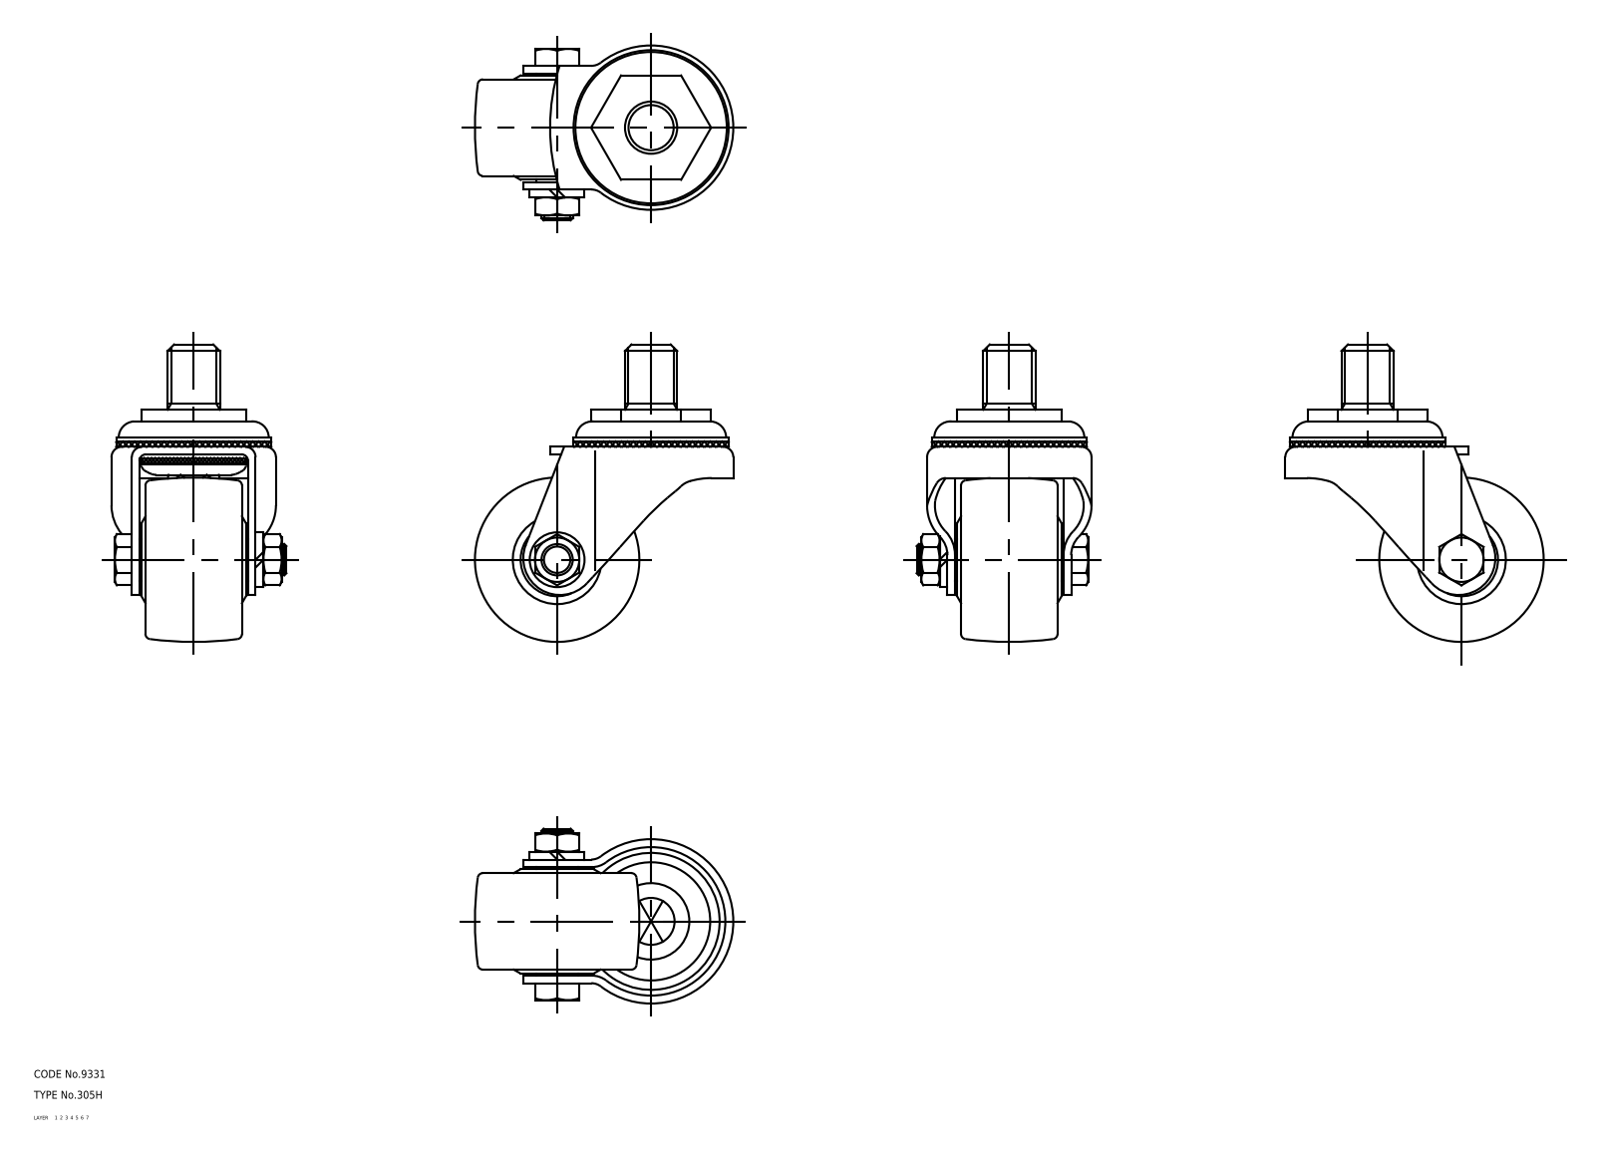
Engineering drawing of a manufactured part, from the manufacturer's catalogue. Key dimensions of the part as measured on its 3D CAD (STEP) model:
Part name (STEP PRODUCT): 67121938; 67121951; 67121964; 67121977
STEP written by: CADfix (AUTOMOTIVE_DESIGN)
Units: millimetres
Bodies: 4 solids, 205 faces (0 planar, 0 cylindrical, 205 other)
Overall size (bounding box): 114 × 98.85 × 66.85
Volume: 191 137 mm³ · Surface area: 45 204 mm²
